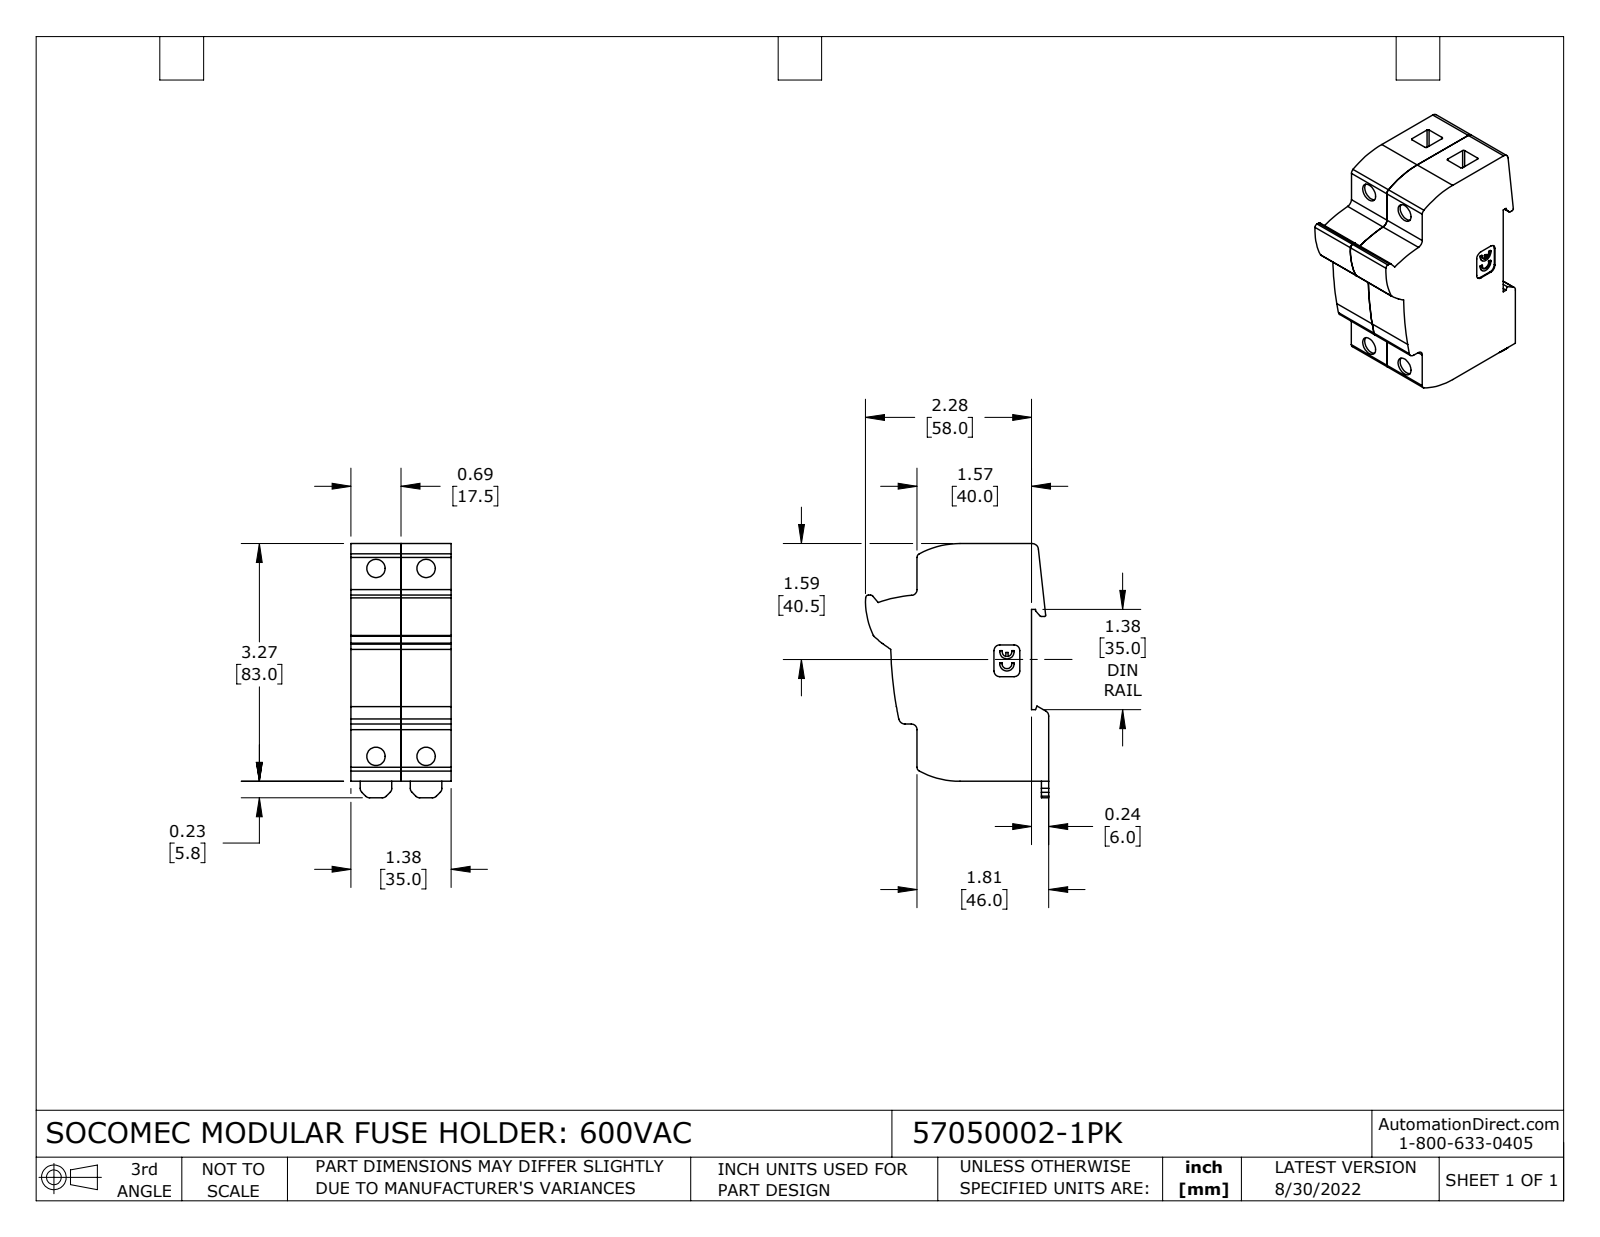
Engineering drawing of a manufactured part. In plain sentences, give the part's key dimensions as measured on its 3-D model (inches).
The part is named "57050002-1PK". Its 3-D file was written by "SolidWorks 2021 (CONFIG_CONTROL_DESIGN)". It is 2 solids with 210 faces: 104 planar, 106 cylindrical and 0 other. Overall it measures 3.496 by 2.52 by 1.378 inches. Its volume is 8.458 cubic inches and its surface area 42.66 square inches. Round holes: 4 of diameter 0.252. Partial cylindrical surfaces (rounded edges, fillets, slot ends): 15 of radius 0.079, 9 of radius 0.02, 4 of radius 0.039, 2 of radius 0.059, 2 of radius 0.067, 2 of radius 0.087, 2 of radius 0.098, 2 of radius 1.186. The main face-to-face distances are 0.689, 1.378, 0.236, 1.575, 3.268, 1.811, 0.199, 0.49, 0.888, 1.179. The hole center spacings are 0.689, 2.583, 2.673.
